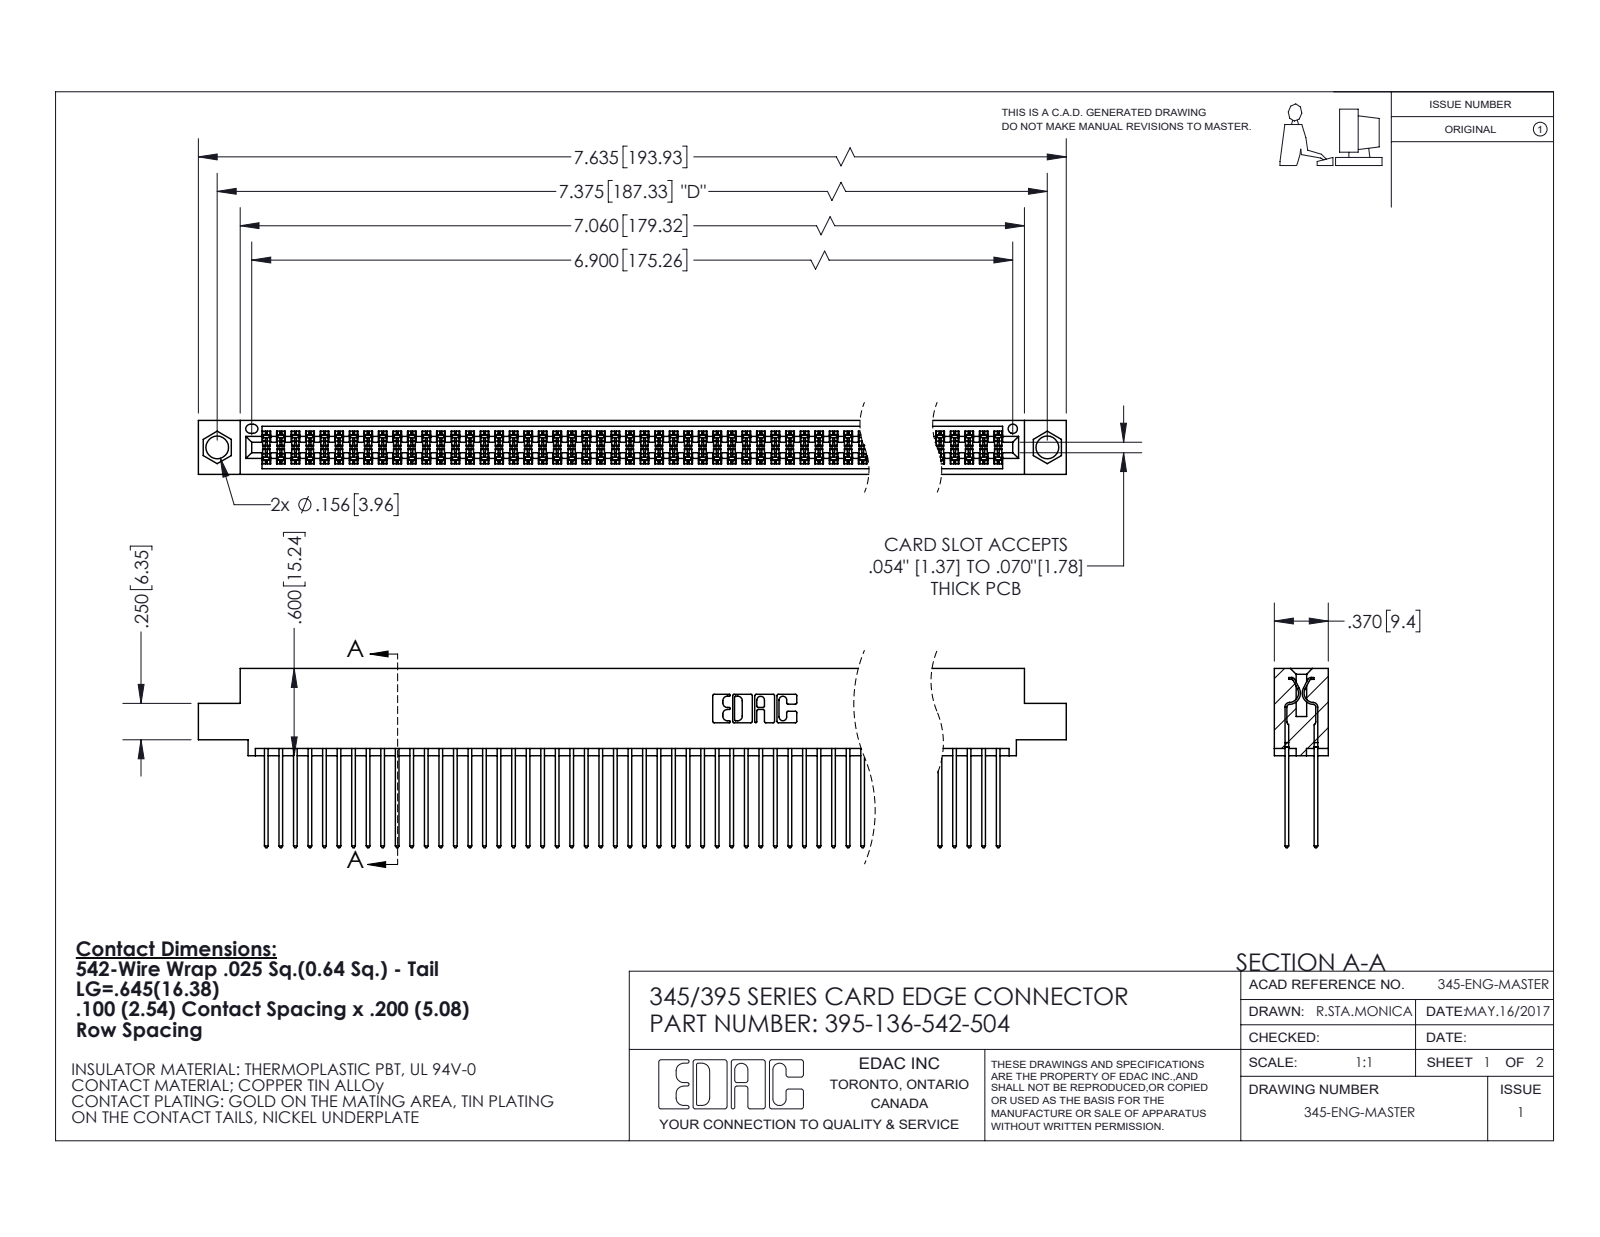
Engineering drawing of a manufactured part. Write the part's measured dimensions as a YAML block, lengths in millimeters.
part_name: "345 Part_0.110 Offset - 0.156 Dia-TI; 345-292-001_345-293-142; 395-136-542-504"
step_written_by: "SolidWorks 2020 (CONFIG_CONTROL_DESIGN)"
units: millimeters
bodies: {solids: 137, faces: 6944, planar: 4586, cylindrical: 2358, other: 0}
overall_size: [193.9, 31.3, 9.4]
volume: 19530
surface_area: 32280
round_holes:
  - {diameter: 4, count: 2}
  - {diameter: 1.6, count: 1}
partial_cylinders:
  - {radius: 0.2, count: 204}
  - {radius: 0.3, count: 136}
  - {radius: 0.3, count: 22}
  - {radius: 0.2, count: 6}
  - {radius: 0.8, count: 6}
  - {radius: 0.7, count: 3}
  - {radius: 0.4, count: 2}
  - {radius: 0.5, count: 2}
face_to_face_distances: [1.8, 7.6, 5.1, 2.5, 6.9, 0.6, 5.7, 9.4, 4.4, 3.8]
hole_center_spacings: [6.9, 181.3, 187.3]
